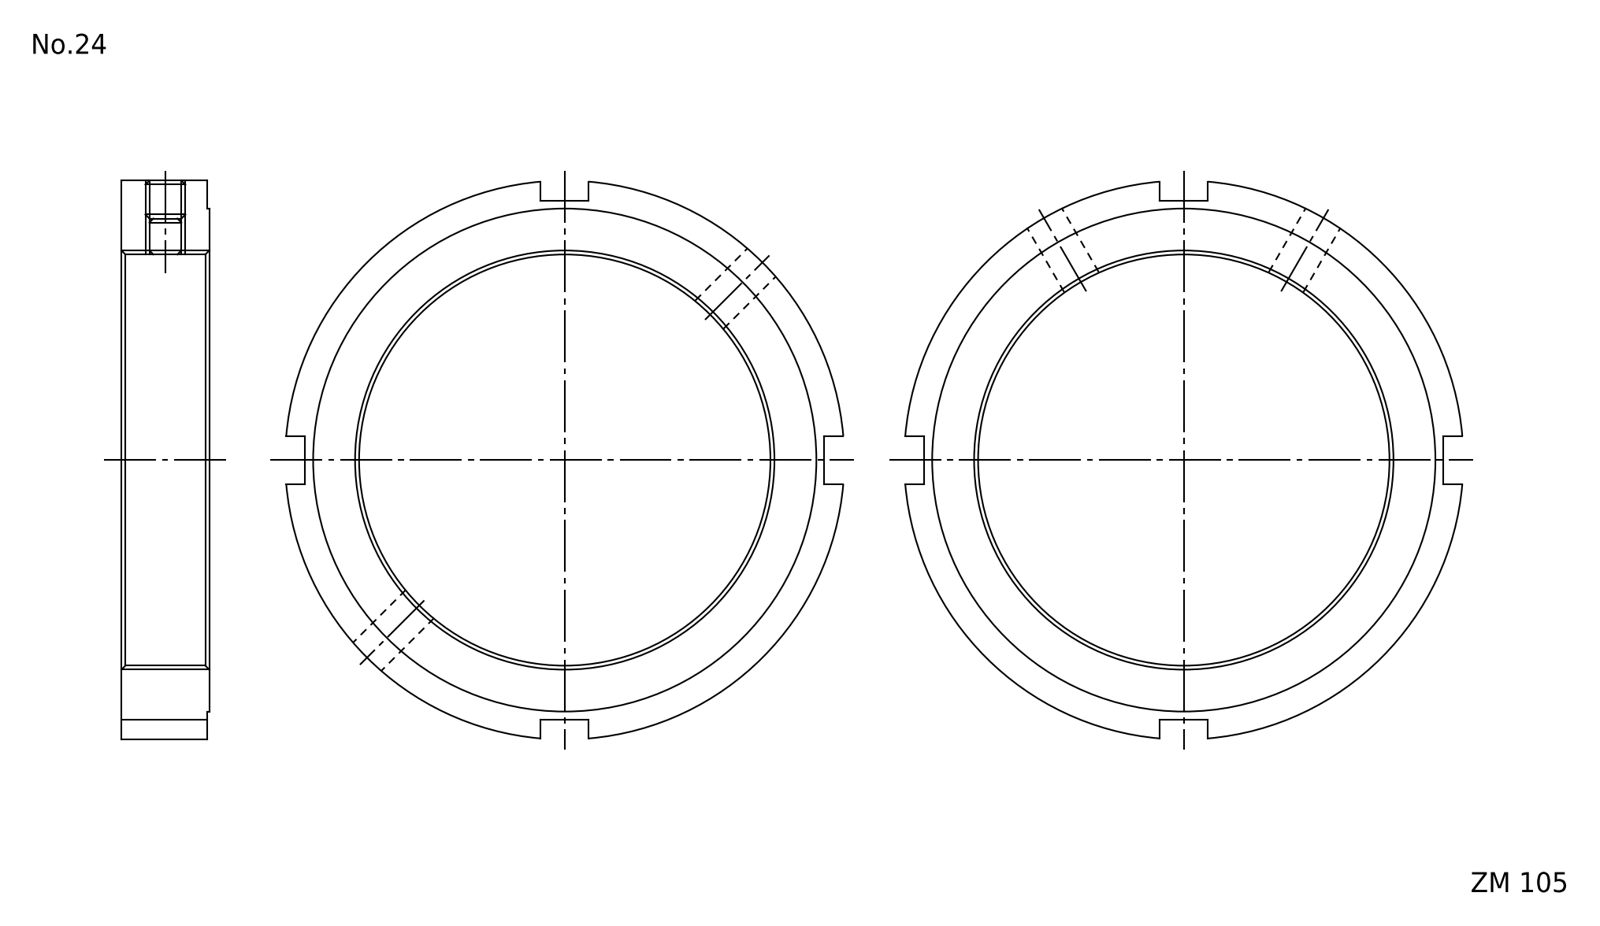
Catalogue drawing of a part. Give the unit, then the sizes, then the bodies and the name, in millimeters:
Units: millimetres
Overall size (bounding box): 139.49 × 139.49 × 22
Round holes (diameter × count): ⌀8.38 ×2, ⌀105 ×1
Round bosses / shafts (diameter × count): ⌀140 ×1, ⌀126 ×1
Main face-to-face distances: 22, 0.5, 21.5, 59, 71, 130, 12
Volume: 139 702 mm³ · Surface area: 31 425 mm²
Bodies: 1 solid, 23 faces (15 planar, 8 cylindrical, 0 other)
Part name (STEP PRODUCT): FKD ZM105
STEP written by: Autodesk Inventor 2011 (AUTOMOTIVE_DESIGN)
